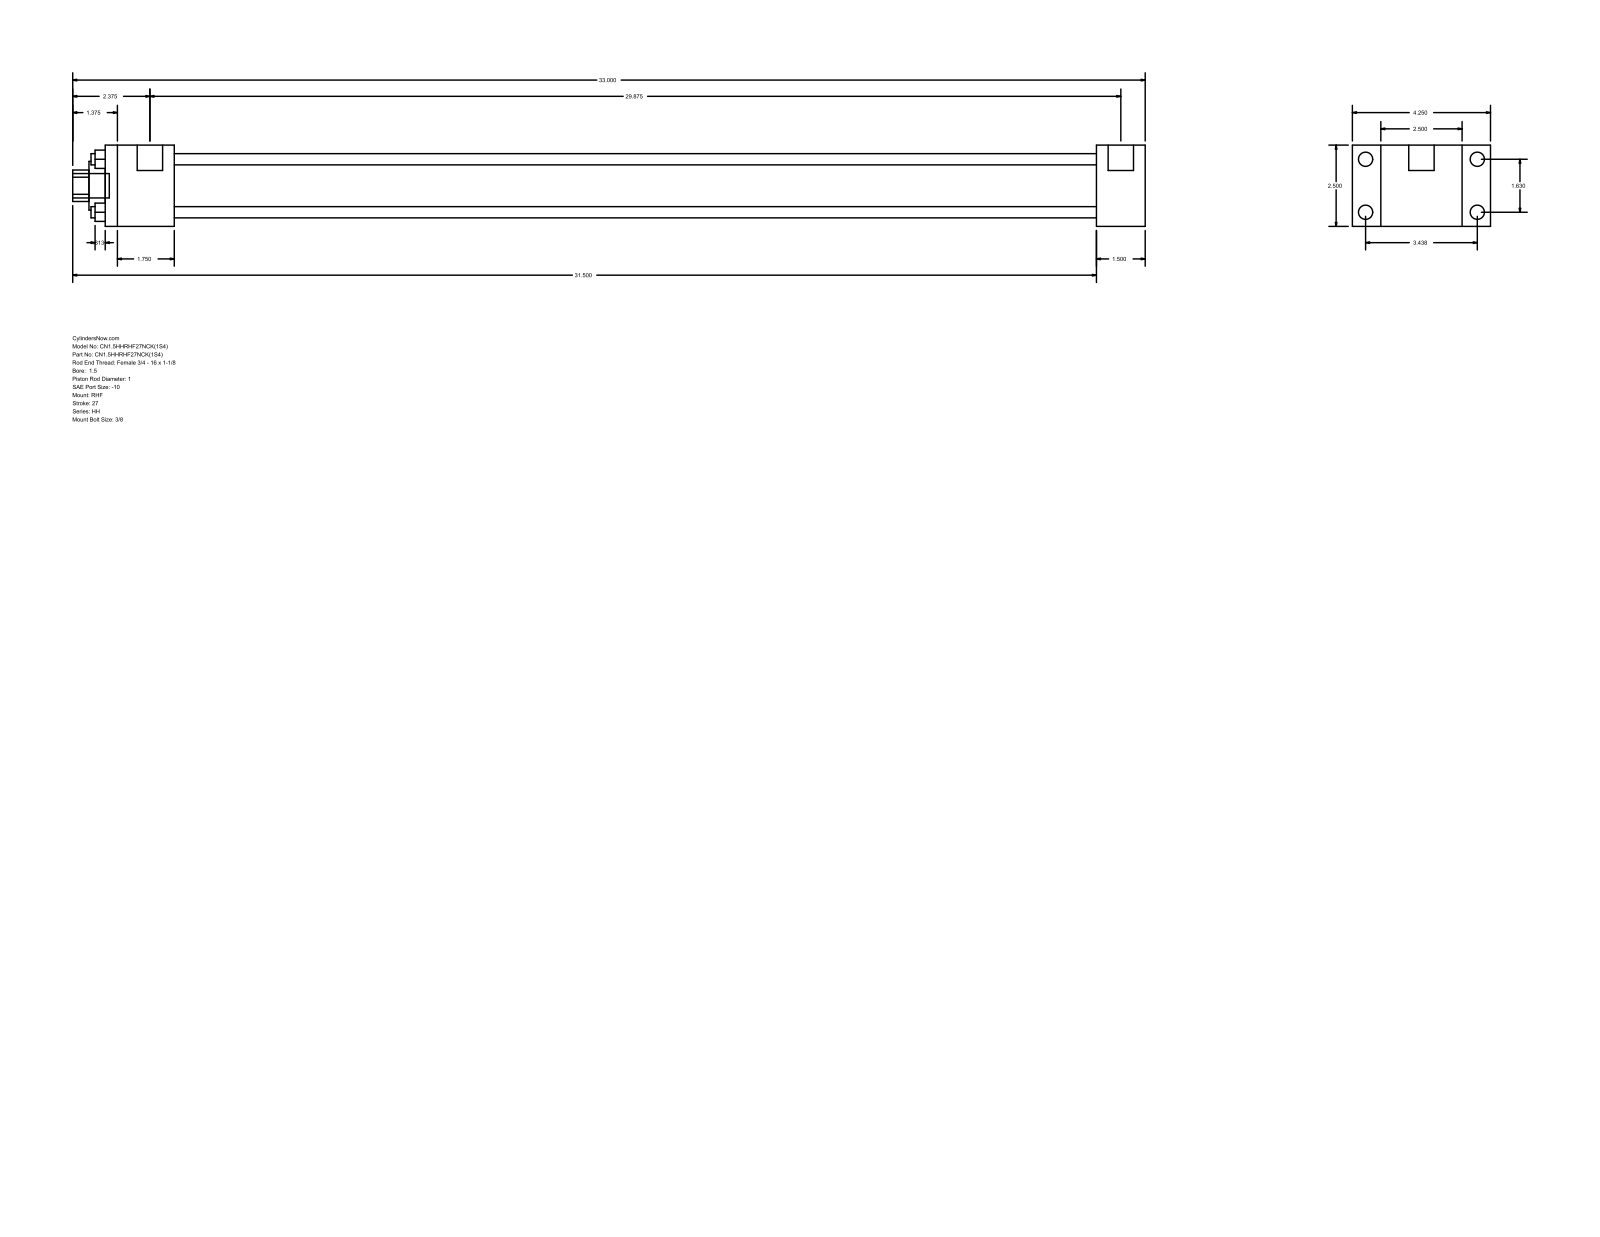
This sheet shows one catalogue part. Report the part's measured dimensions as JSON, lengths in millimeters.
{"part_name": "HH_RHF__0150_1", "step_written_by": "GSSL Pune (CONFIG_CONTROL_DESIGN)", "units": "millimeters", "bodies": {"solids": 0, "faces": 88, "planar": 60, "cylindrical": 28, "other": 0}, "overall_size": [838.2, 107.95, 63.5], "round_holes": [[8.76, 4], [25.4, 1], [38.1, 1], [44.45, 1]], "round_bosses_or_shafts": [[11.13, 4], [5.56, 4], [19.84, 2], [19.05, 1]], "partial_cylinders_radius": [[12.29, 1]], "face_to_face_distances": [63.5, 22.23, 85.73, 38.1, 107.96, 720.72, 758.82, 53.98, 774.7, 812.8], "hole_center_spacings": [29.27, 41.4, 58.55]}
